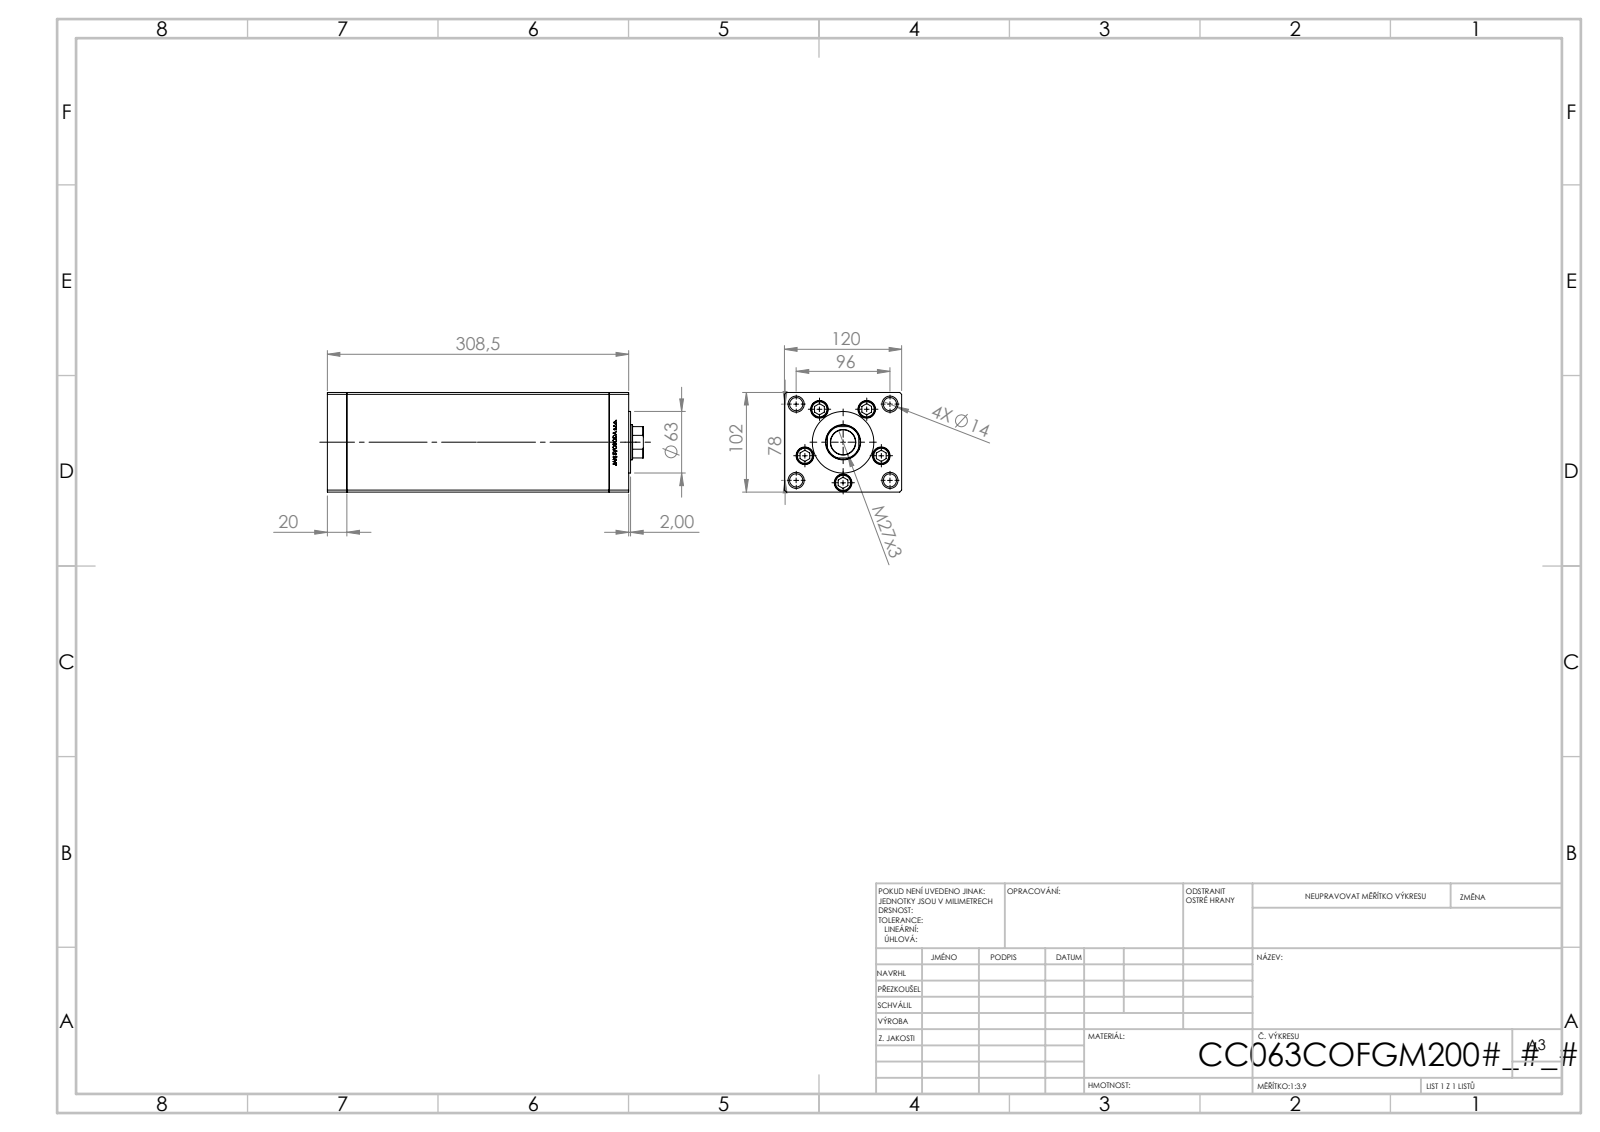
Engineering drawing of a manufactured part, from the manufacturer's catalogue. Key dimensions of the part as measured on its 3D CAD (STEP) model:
Part name (STEP PRODUCT): V220C_C MIDDLE; V220C_VC_C; V220C BACK_C; ALLEN BOLT (+1 more)
STEP written by: SolidWorks 2019 (CONFIG_CONTROL_DESIGN)
Units: millimetres
Bodies: 13 solids, 1165 faces (542 planar, 161 cylindrical, 462 other)
Overall size (bounding box): 323.5 × 120 × 102
Volume: 3 135 000 mm³ · Surface area: 375 908 mm²
Round holes (diameter × count): ⌀13.5 ×9, ⌀18 ×5, ⌀12 ×4, ⌀16.5 ×4, ⌀17 ×1, ⌀25.5 ×1, ⌀36 ×1
Round bosses / shafts (diameter × count): ⌀8 ×5, ⌀17 ×4, ⌀63 ×1
Partial cylindrical surfaces — rounded edges, fillets, slot ends (radius × count): R0.93 ×2, R17.5 ×1
Main face-to-face distances: 120, 102, 20, 268.5, 288.5, 34.25, 308.5, 274.25, 254.25, 14.25
Hole centre spacings: 41.5, 61.85, 24.39, 26.69, 47.92, 48.07, 49.84, 53.57
